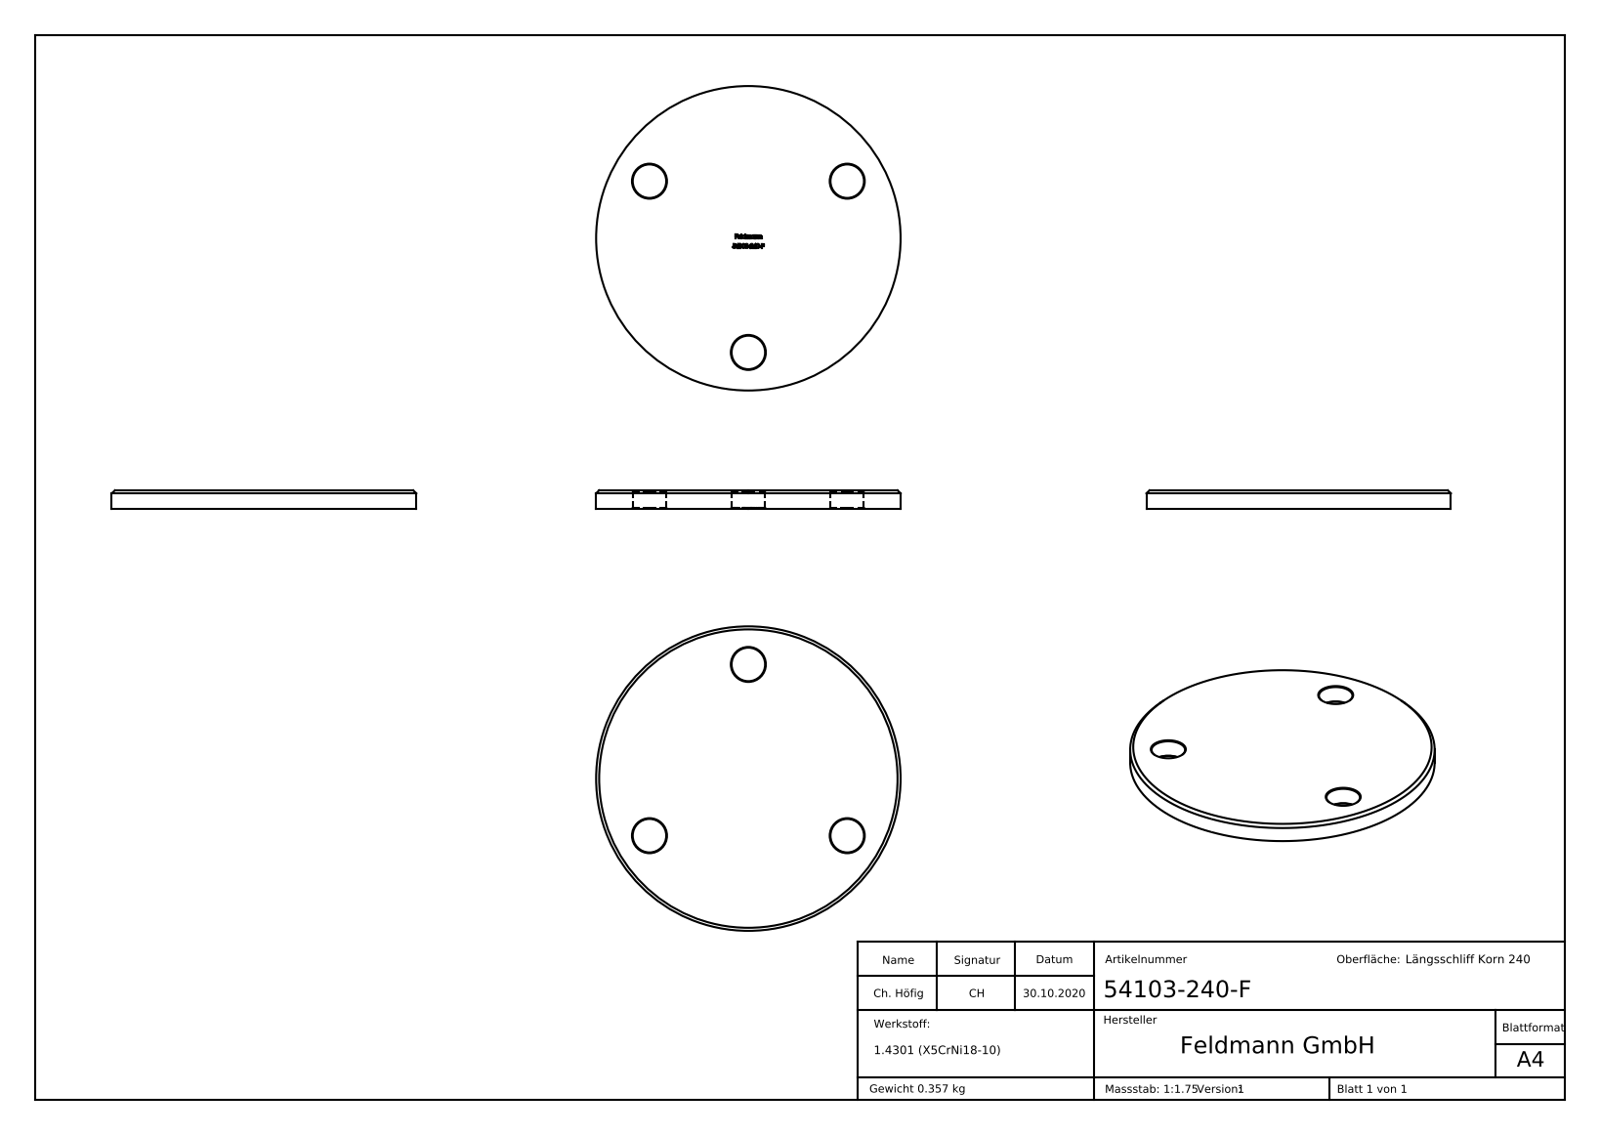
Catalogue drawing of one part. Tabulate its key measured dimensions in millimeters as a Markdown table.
| quantity | value |
| --- | --- |
| part name | 54103-240-F |
| STEP written by | SolidWorks 2018 (CONFIG_CONTROL_DESIGN) |
| units | millimeters |
| bodies | 1 solid, 263 faces (147 planar, 8 cylindrical, 108 other) |
| overall size | 100 × 100 × 6 |
| volume | 45 250 mm³ |
| surface area | 17 440 mm² |
| round holes (diameter × count) | 11 × 3 |
| round bosses / shafts (diameter × count) | 100 × 1 |
| main face-to-face distances | 6, 5.9, 1.65, 3.19, 2.01, 2.02, 6.67, 0.31, 2.97, 3.39 |
| hole center spacings | 64.95, 64.96 |
